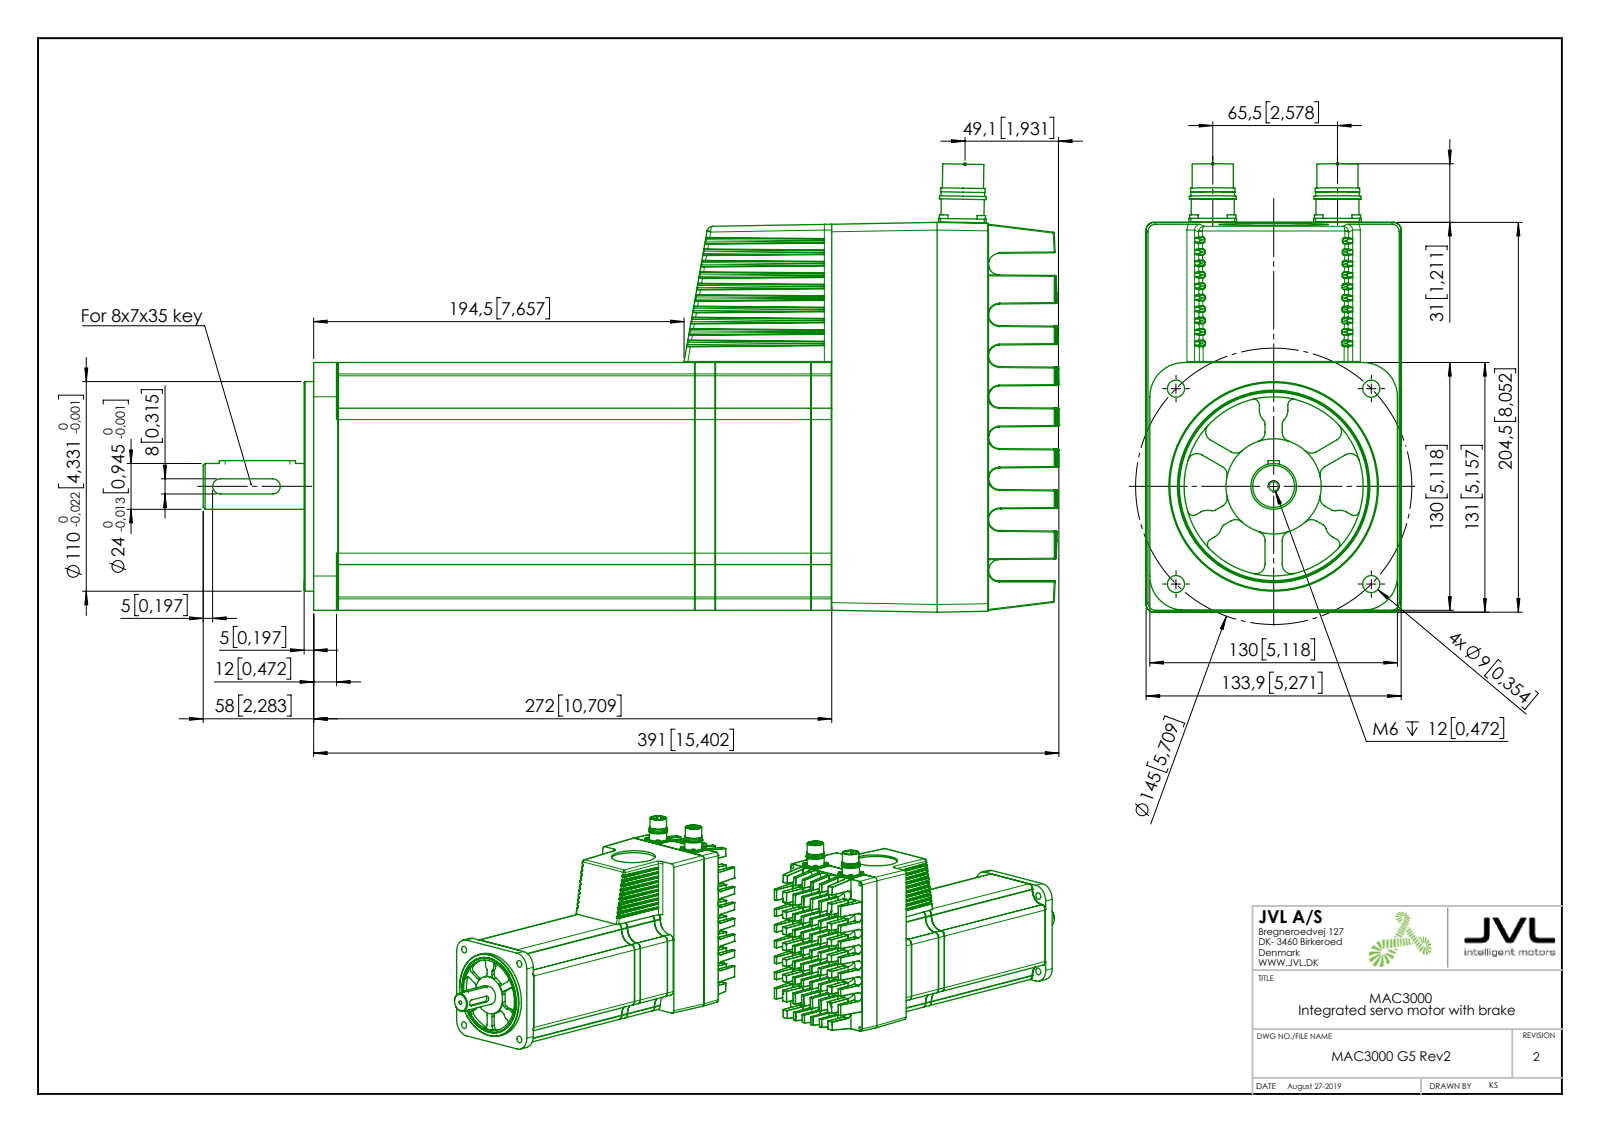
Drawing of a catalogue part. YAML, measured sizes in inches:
part_name: "M23 female; Front cover S; M23 male; Key (+8 more)"
step_written_by: "SolidWorks 2018 (AUTOMOTIVE_DESIGN)"
units: inches
bodies: {solids: 13, faces: 2506, planar: 791, cylindrical: 1010, other: 705}
overall_size: [17.688, 9.263, 5.271]
volume: 422.7
surface_area: 933.6
round_holes:
  - {diameter: 0.098, count: 8}
  - {diameter: 0.079, count: 5}
  - {diameter: 0.169, count: 4}
  - {diameter: 0.354, count: 4}
  - {diameter: 0.787, count: 2}
  - {diameter: 0.795, count: 2}
  - {diameter: 0.181, count: 1}
  - {diameter: 0.197, count: 1}
  - {diameter: 2.269, count: 1}
  - {diameter: 3.701, count: 1}
  - {diameter: 3.937, count: 1}
  - {diameter: 4.606, count: 1}
round_bosses_or_shafts:
  - {diameter: 0.177, count: 8}
  - {diameter: 0.079, count: 5}
  - {diameter: 0.965, count: 2}
  - {diameter: 0.917, count: 2}
  - {diameter: 0.902, count: 2}
  - {diameter: 0.89, count: 2}
  - {diameter: 0.85, count: 2}
  - {diameter: 4.409, count: 1}
partial_cylinders:
  - {radius: 0.02, count: 297}
  - {radius: 0.012, count: 92}
  - {radius: 0.031, count: 40}
  - {radius: 0.197, count: 18}
  - {radius: 0.118, count: 17}
  - {radius: 0.157, count: 12}
  - {radius: 0.024, count: 10}
  - {radius: 0.236, count: 8}
face_to_face_distances: [2.402, 0.433, 5.118, 2.177, 10.197, 12.374, 7.362, 2.835, 5.012, 7.795]
hole_center_spacings: [0.557, 0.787, 2.578, 0.278, 1.113, 2.219, 2.696, 2.855]
